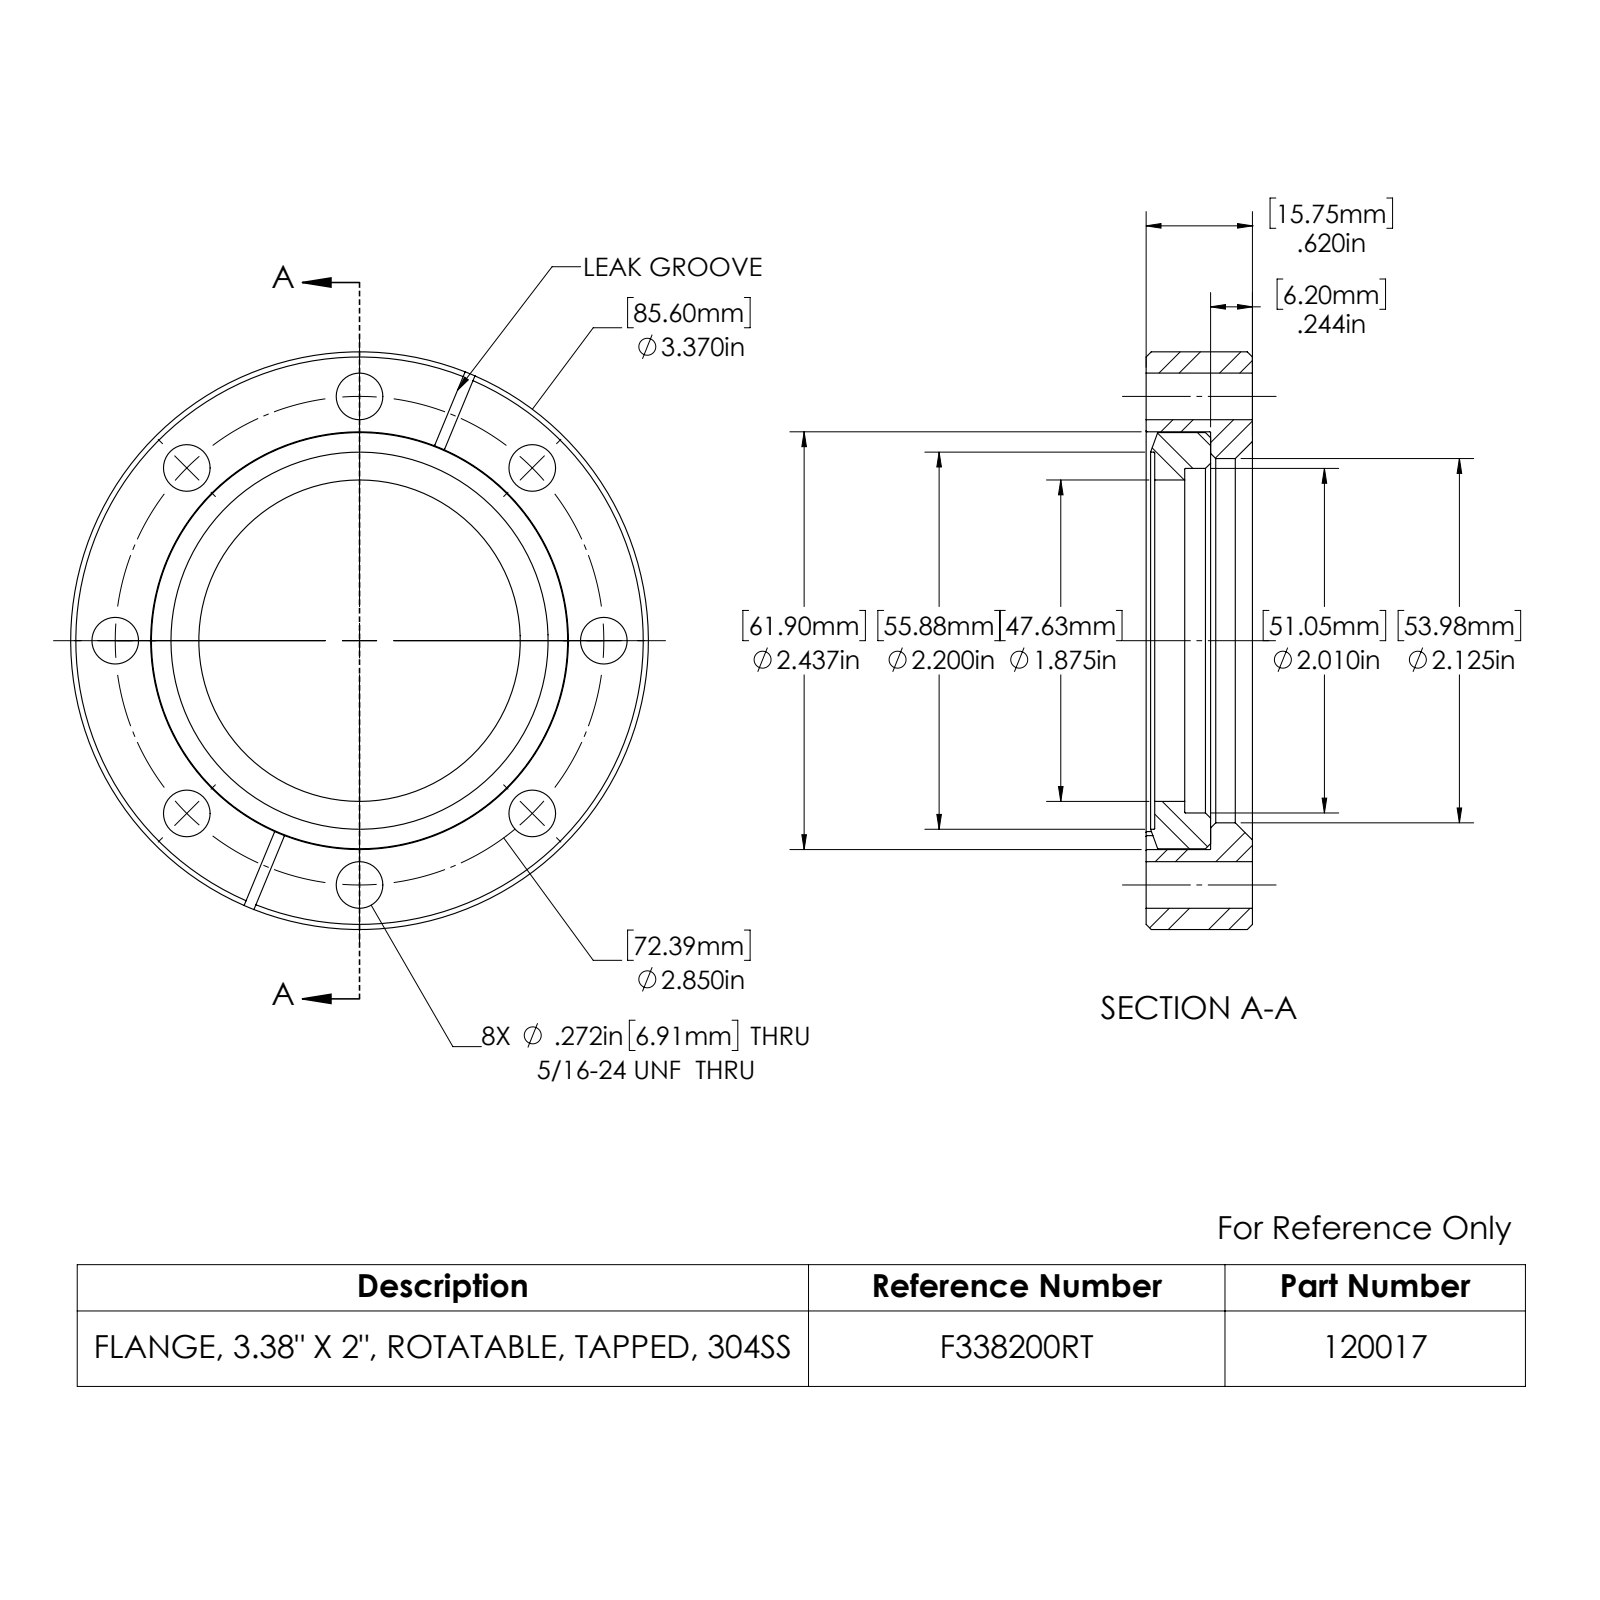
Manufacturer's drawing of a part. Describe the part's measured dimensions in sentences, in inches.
The part is named "920003; 910017; 120017_A". Its 3-D file was written by "SolidWorks 2022 (CONFIG_CONTROL_DESIGN)". It is 2 solids with 67 faces: 13 planar, 30 cylindrical and 24 other. Overall it measures 3.37 by 3.37 by 0.62 inches. Its volume is 3.116 cubic inches and its surface area 32.35 square inches. Round holes: 8 of diameter 0.272, 1 of diameter 1.875, 1 of diameter 2.01, 1 of diameter 2.125, 1 of diameter 2.2, 1 of diameter 2.437. Round bosses or shafts: 1 of diameter 3.37, 1 of diameter 2.428. The main face-to-face distances are 0.62, 0.376, 0.244, 0.05, 0.326, 0.57, 0.225, 0.175, 0.151, 0.395. The hole center spacings are 1.091, 2.633, 2.015, 1.425, 1.425, 2.85, 2.015, 1.091.
